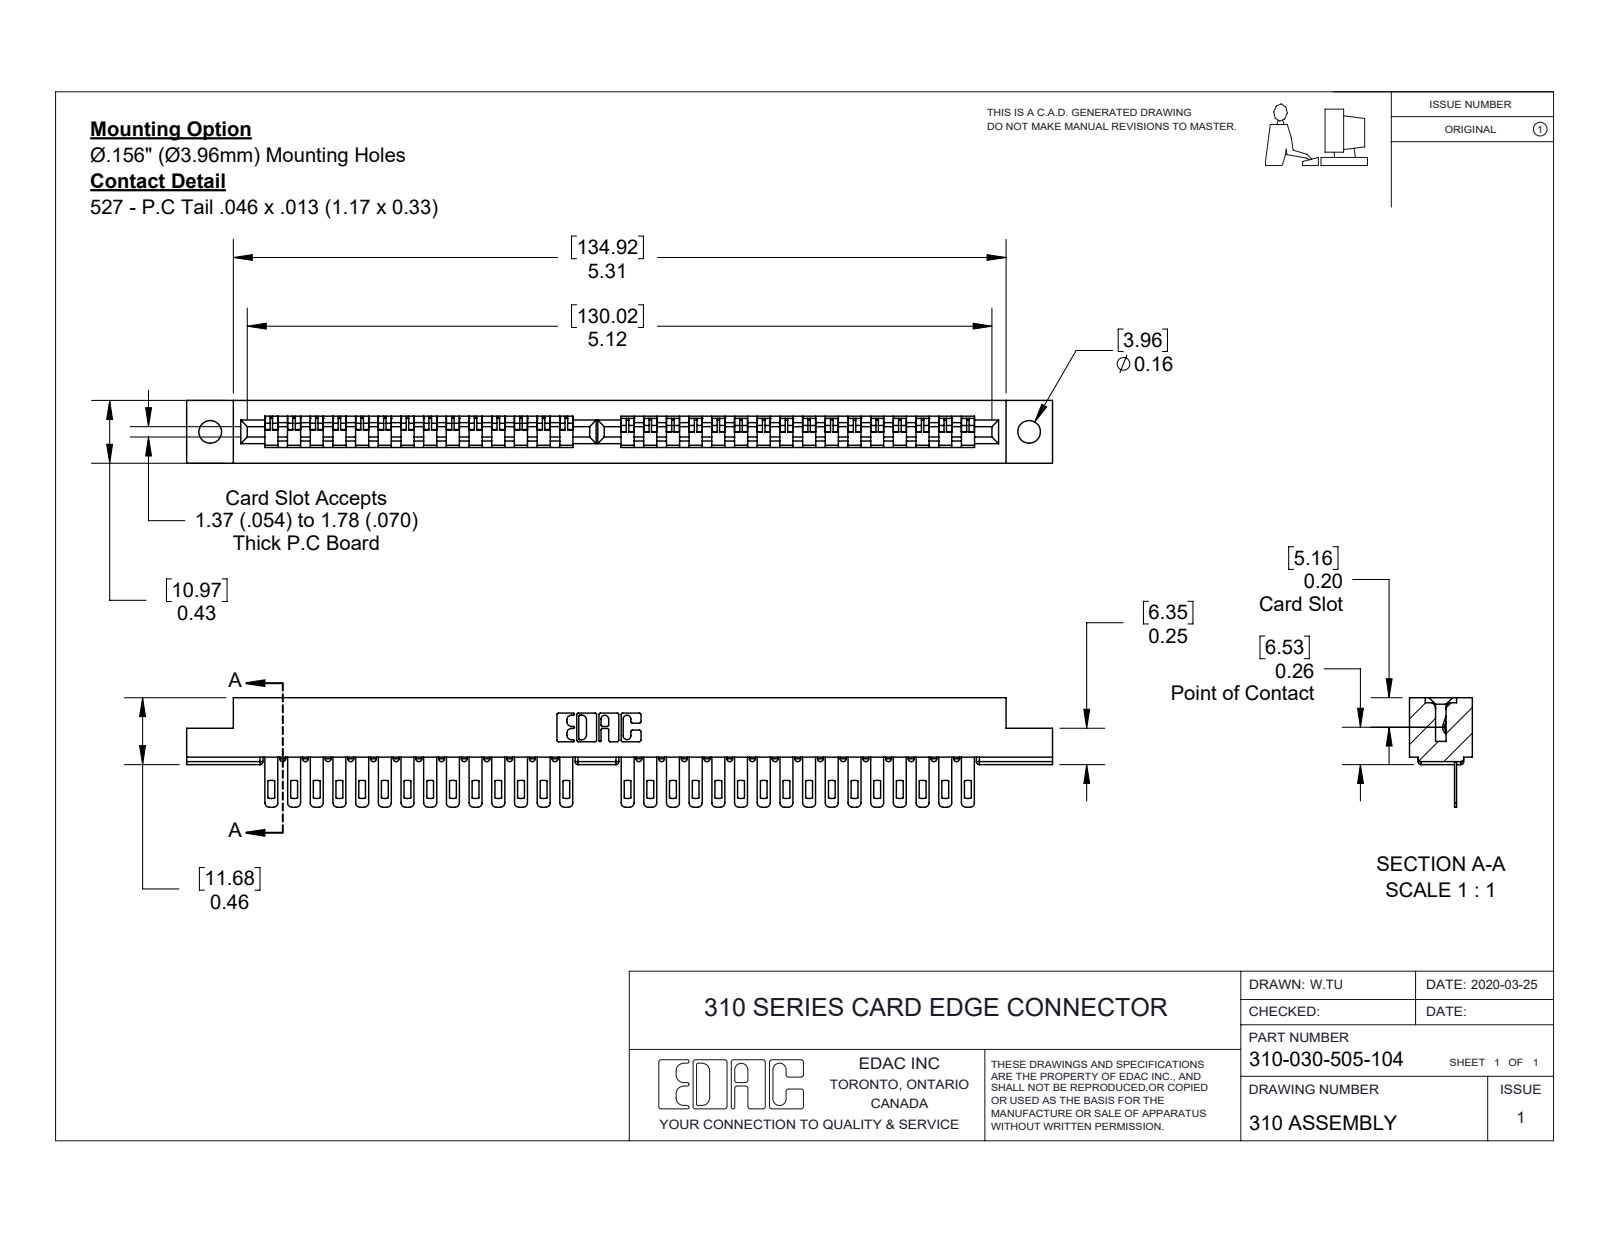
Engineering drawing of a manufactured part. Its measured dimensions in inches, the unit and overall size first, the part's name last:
Units: inches
Overall size (bounding box): 5.953 × 0.753 × 0.432
Round holes (diameter × count): ⌀0.156 ×2
Partial cylindrical surfaces — rounded edges, fillets, slot ends (radius × count): R0.02 ×98, R0.03 ×60, R0.063 ×30, R0.01 ×22, R0.007 ×6, R0.031 ×6, R0.026 ×3, R0.012 ×2
Main face-to-face distances: 0.109, 0.324, 0.432, 0.015, 0.013, 0.072, 0.409, 0.215, 0.124, 0.309
Hole centre spacings: 5.63
Volume: 0.77 in³ · Surface area: 23.31 in²
Bodies: 31 solids, 1846 faces (1164 planar, 618 cylindrical, 64 other)
Part name (STEP PRODUCT): 307-290-001_505; 310 Part_.156 Dia. Hole; 310-030-505-104
STEP written by: SolidWorks 2016 (CONFIG_CONTROL_DESIGN)
